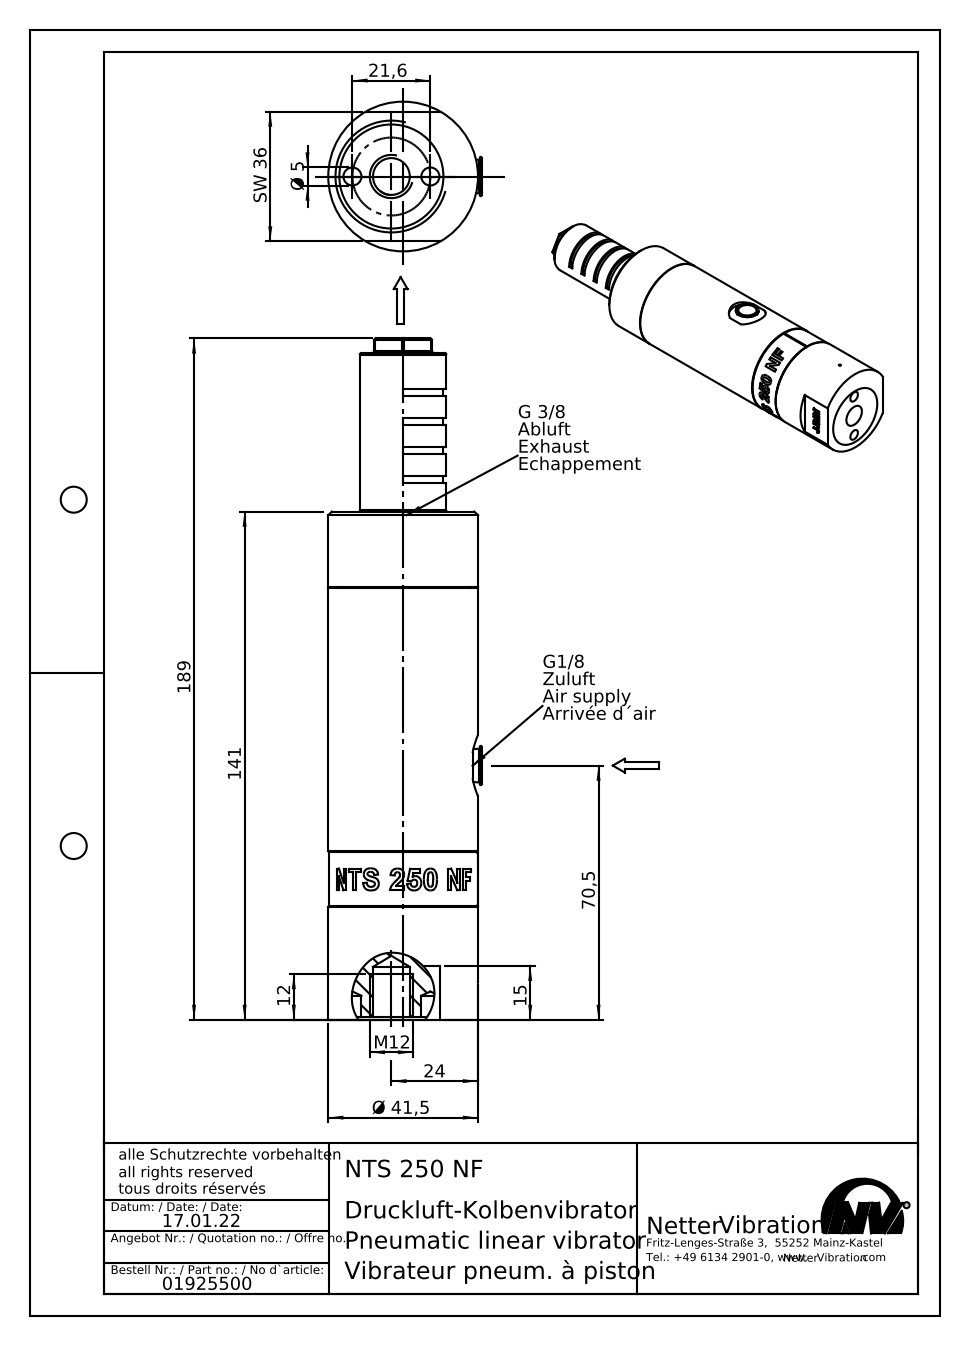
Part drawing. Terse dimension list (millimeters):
name: NTS 250 NF Kolbenvibrator #01925500
written by: SolidWorks 2015 (AUTOMOTIVE_DESIGN)
unit: mm
bodies: 5 solids, 253 faces (50 planar, 158 cylindrical, 45 other)
size: 188.9 × 41.5 × 41.5
volume: 206 717 mm³; area: 43 232 mm²
holes: 4× ⌀3, 2× ⌀5, 1× ⌀1, 1× ⌀8.57, 1× ⌀10.2, 1× ⌀15.25, 1× ⌀15.4, 1× ⌀17.5, 1× ⌀27, 1× ⌀28.84, 1× ⌀36, 1× ⌀40.9
bosses: 1× ⌀41.5, 1× ⌀41.3, 1× ⌀37.4, 1× ⌀37, 1× ⌀35.5, 1× ⌀31, 1× ⌀24, 1× ⌀16.66
rounds: 22× R0.5, 1× R8.5, 1× R11
face distances: 4, 12.7, 120.9, 108.2, 16, 112.2, 18.9, 6.2, 102, 124.9
hole spacings: 10.24, 10.8, 11.16, 14.07, 15, 16.53, 25.98, 26.86
